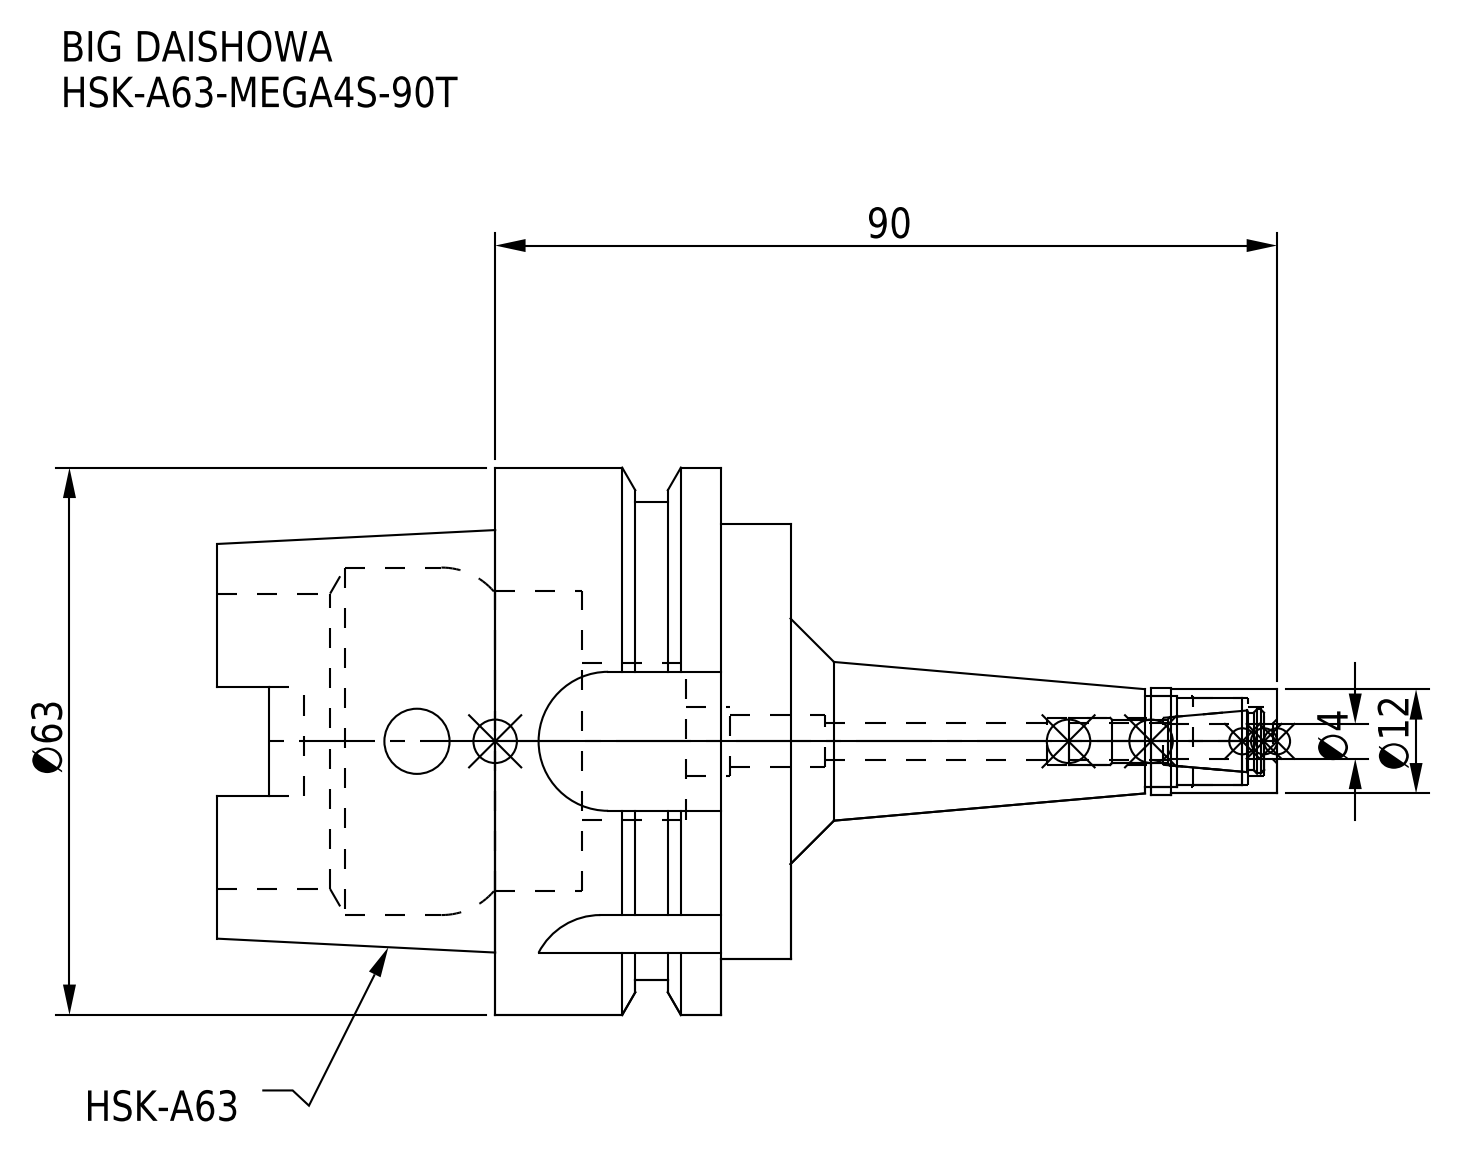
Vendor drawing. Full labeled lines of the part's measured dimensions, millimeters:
Part name (STEP PRODUCT): HSK-A63-MEGA4S-90T; HSK-A63-MEGA4S-90T_1.stp; HA63MS04090T-040_ASM.stp; MGN4S_1.stp (+3 more)
STEP written by: SolidWorks 2019 (CONFIG_CONTROL_DESIGN)
Units: millimetres
Bodies: 2 solids, 125 faces (48 planar, 55 cylindrical, 22 other)
Overall size (bounding box): 122 × 63 × 63
Volume: 106 269 mm³ · Surface area: 27 859 mm²
Round holes (diameter × count): ⌀4.1 ×1, ⌀4.2 ×1, ⌀5.4 ×1, ⌀6 ×1, ⌀7.5 ×1, ⌀8 ×1, ⌀10 ×1, ⌀10.5 ×1, ⌀18 ×1, ⌀34 ×1, ⌀34.5 ×1, ⌀40 ×1
Round bosses / shafts (diameter × count): ⌀63 ×1, ⌀55 ×1, ⌀50 ×1, ⌀12.3 ×1, ⌀12 ×1
Partial cylindrical surfaces — rounded edges, fillets, slot ends (radius × count): R2.88 ×4, R8 ×4
Main face-to-face distances: 34, 26, 8, 16.05, 24.05, 9.95, 66, 58, 41.95, 32
